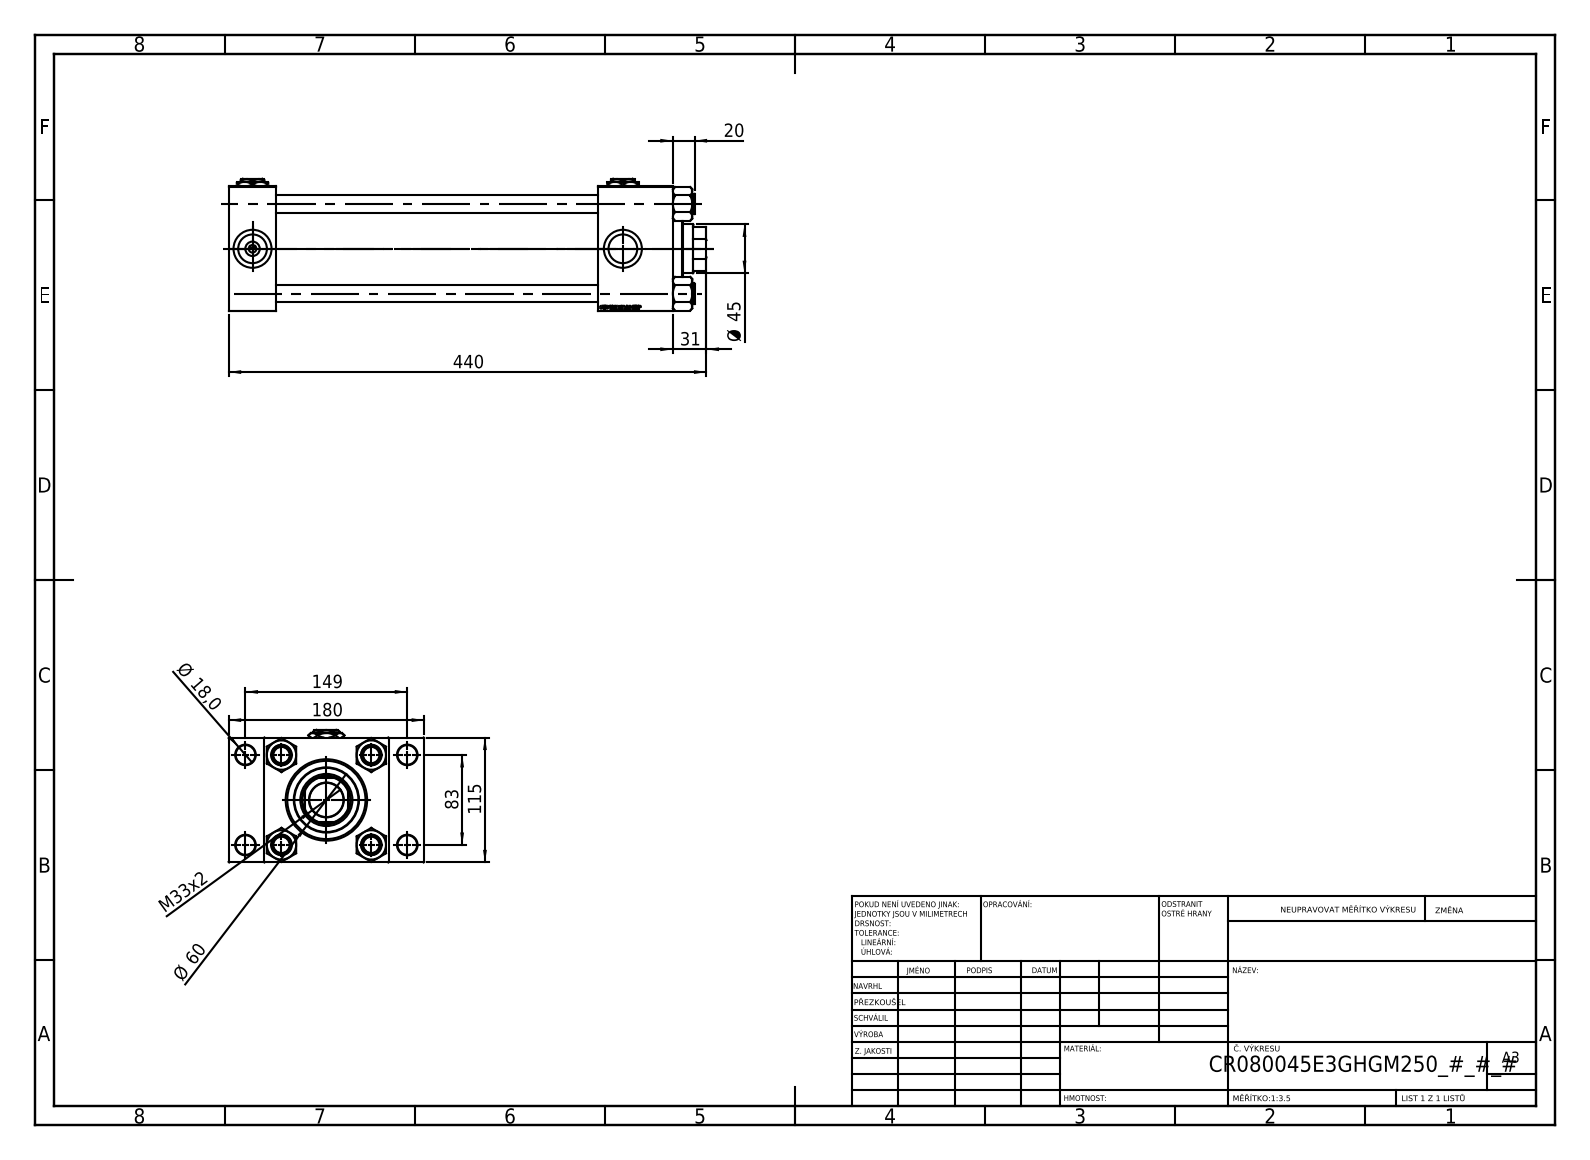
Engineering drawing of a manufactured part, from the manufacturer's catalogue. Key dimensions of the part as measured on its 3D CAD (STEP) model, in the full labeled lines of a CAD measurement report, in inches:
Part name (STEP PRODUCT): NUT_M5_E; V215_VC_A; V215CR_E_Body; V215CR_VCP_E (+2 more)
STEP written by: SolidWorks 2019 (CONFIG_CONTROL_DESIGN)
Units: inches
Bodies: 13 solids, 1284 faces (593 planar, 97 cylindrical, 594 other)
Overall size (bounding box): 17.323 × 7.087 × 4.803
Volume: 172.9 in³ · Surface area: 808.3 in²
Round holes (diameter × count): ⌀0.63 ×4, ⌀0.709 ×4, ⌀1.041 ×4, ⌀1.378 ×4, ⌀0.276 ×3, ⌀1.24 ×1, ⌀1.772 ×1, ⌀1.89 ×1, ⌀2.402 ×1, ⌀2.835 ×1, ⌀3.15 ×1
Round bosses / shafts (diameter × count): ⌀0.748 ×4, ⌀3.386 ×1, ⌀2.362 ×1
Partial cylindrical surfaces — rounded edges, fillets, slot ends (radius × count): R0.866 ×1
Main face-to-face distances: 4.528, 1.732, 16.102, 14.37, 1.28, 5.807, 2.717, 13.386, 11.654, 7.087
Hole centre spacings: 1.305, 2.302, 3.256, 3.357, 3.513, 4.561, 5.607, 3.268
